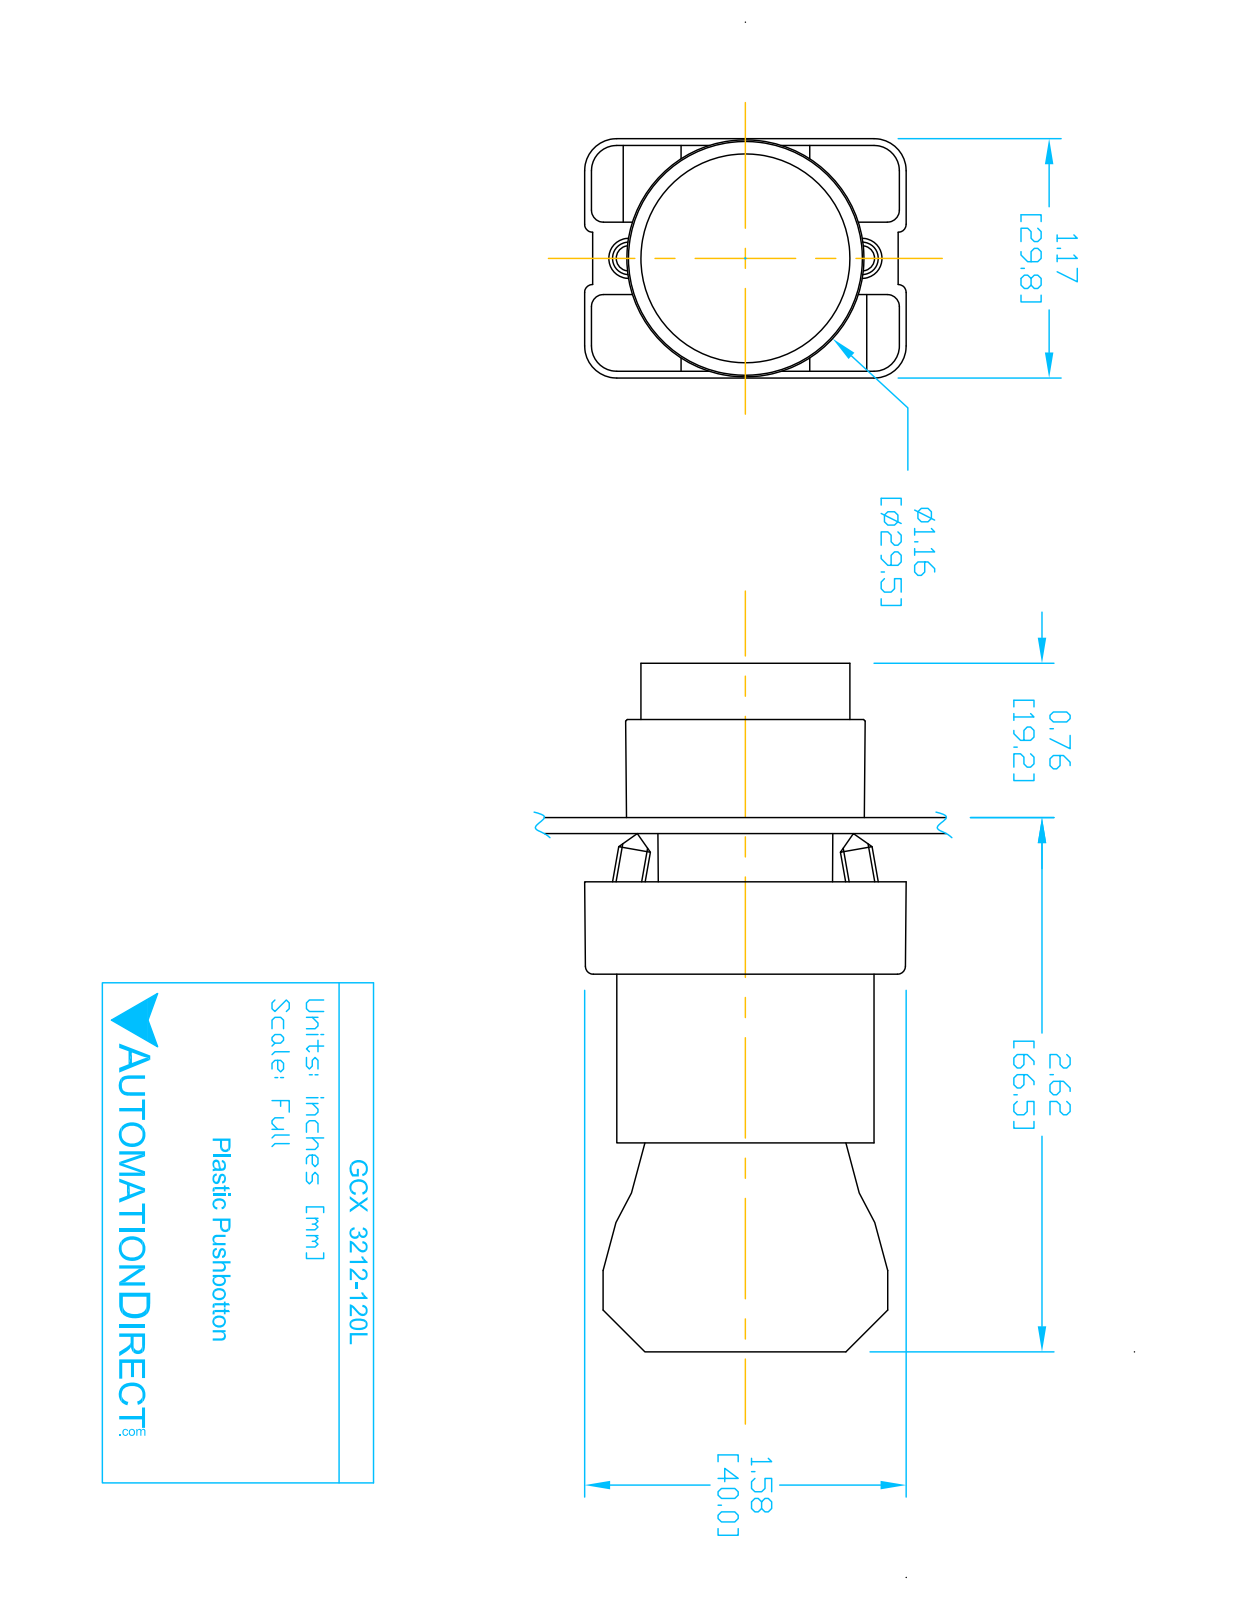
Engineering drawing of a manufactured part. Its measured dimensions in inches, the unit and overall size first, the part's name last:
Units: inches
Overall size (bounding box): 3.319 × 1.581 × 1.177
Round holes (diameter × count): ⌀0.079 ×2, ⌀0.124 ×2, ⌀0.13 ×2, ⌀0.087 ×1, ⌀0.197 ×1, ⌀0.469 ×1, ⌀0.878 ×1, ⌀0.888 ×1, ⌀1.024 ×1
Round bosses / shafts (diameter × count): ⌀0.157 ×4, ⌀1.175 ×1, ⌀1.004 ×1, ⌀0.945 ×1, ⌀0.856 ×1, ⌀0.78 ×1, ⌀0.504 ×1
Partial cylindrical surfaces — rounded edges, fillets, slot ends (radius × count): R0.059 ×24, R0.041 ×12, R0.124 ×12, R0.157 ×12, R0.039 ×8, R0.128 ×2, R0.02 ×1, R0.063 ×1
Main face-to-face distances: 0.827, 0.579, 1.171, 2.02, 1.193, 0.031, 0.033, 0.573, 1.165, 0.593
Hole centre spacings: 0.236, 0.544, 0.472, 0.49
Volume: 2.721 in³ · Surface area: 36.32 in²
Bodies: 7 solids, 425 faces (250 planar, 144 cylindrical, 31 other)
Part name (STEP PRODUCT): ECX3029-2; GCX3212L OPERATOR; GCX3212-120L; ECX1050 (+1 more)
STEP written by: SolidWorks 2016 (AUTOMOTIVE_DESIGN)
